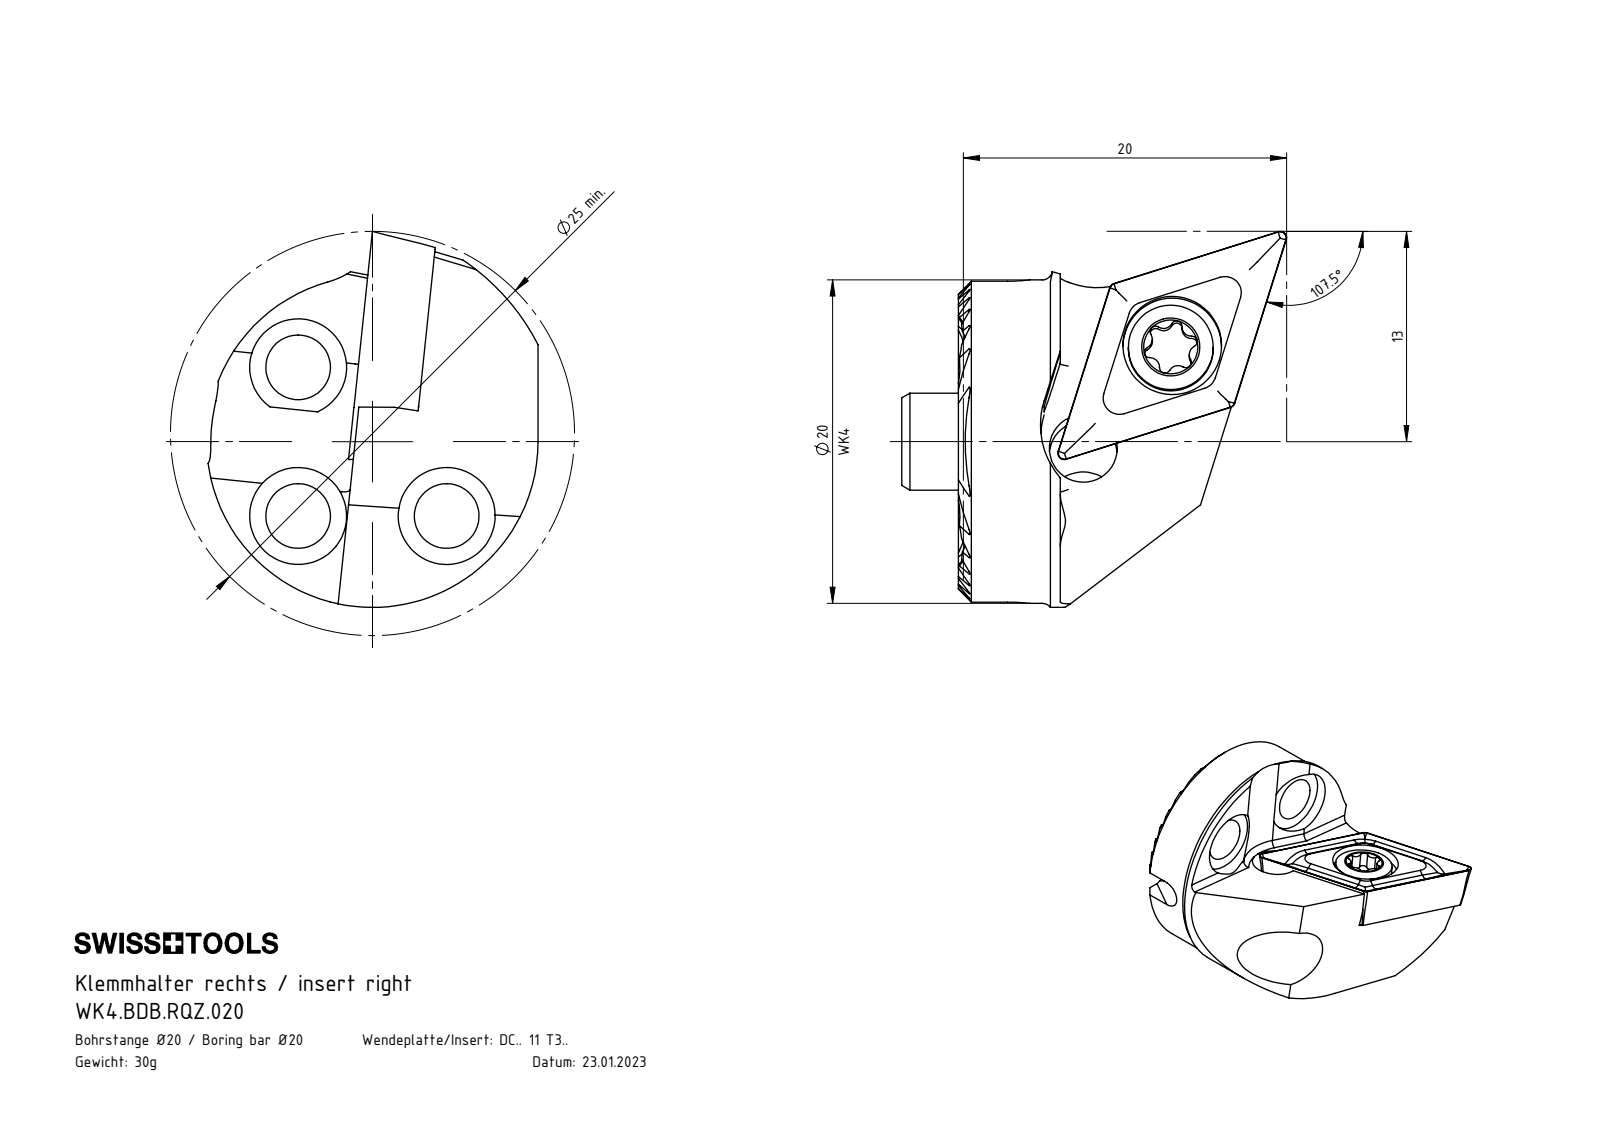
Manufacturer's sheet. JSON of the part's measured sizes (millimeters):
{"part_name": "WK4-BDB.RQZ.020_A; WK3-ER1.001.006_A_Fertigbearbeitung; WCB-ER2.001.009_A; WK4.BDB.RQZ.020 (+1 more)", "step_written_by": "SolidWorks 2017 (AUTOMOTIVE_DESIGN)", "units": "millimeters", "bodies": {"solids": 4, "faces": 340, "planar": 140, "cylindrical": 124, "other": 76}, "overall_size": [23.8, 23.26, 20.41], "volume_mm3": 3028, "surface_area_mm2": 2836, "round_holes": [[4, 3], [6, 3], [4.2, 2], [3.3, 1], [4.4, 1], [5.98, 1], [6.1, 1]], "round_bosses_or_shafts": [[20, 1], [6, 1], [5.25, 1], [4, 1]], "partial_cylinders_radius": [[0.12, 16], [0.34, 6], [0.59, 6], [5, 3], [0.5, 2], [10.25, 1], [14, 1]], "face_to_face_distances": [4.33, 1.08, 3.25, 2.17, 5.41, 3.67, 8.66, 2.16, 7.58, 6.5], "hole_center_spacings": [6.51, 9.2, 8.3, 8.42, 13.01]}
